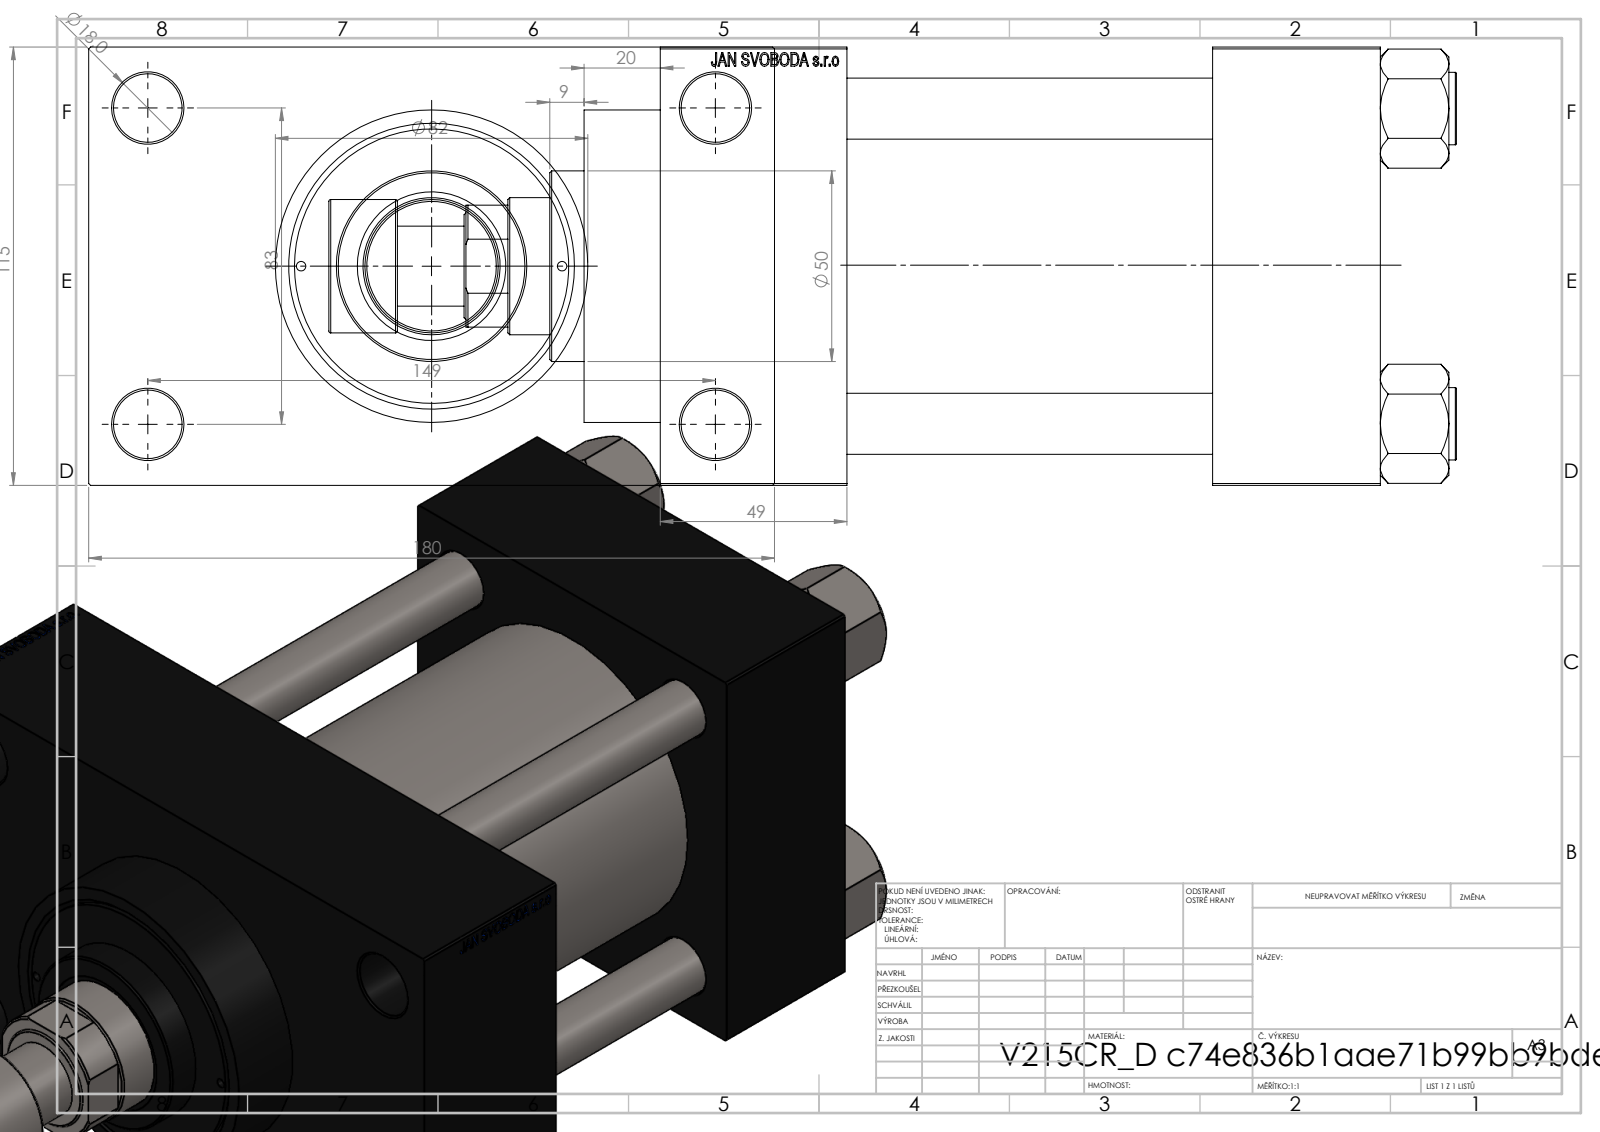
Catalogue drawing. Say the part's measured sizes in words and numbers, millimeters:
The part is named "V215CR_D_Body; V215_VC_A; V215CR_VCP_D; V215CR_D_TYCINKA (+2 more)". Its 3-D file was written by "SolidWorks 2019 (CONFIG_CONTROL_DESIGN)". It is 12 solids with 1173 faces: 551 planar, 96 cylindrical and 526 other. Overall it measures 296 by 180 by 115 millimeters. Its volume is 2 081 000 cubic millimeters and its surface area 327 114 square millimeters. Round holes: 4 of diameter 16, 4 of diameter 18, 2 of diameter 2.5, 2 of diameter 7, 2 of diameter 26.44, 2 of diameter 35, 1 of diameter 25.5, 1 of diameter 36, 1 of diameter 39, 1 of diameter 61, 1 of diameter 72, 1 of diameter 80. Round bosses or shafts: 4 of diameter 19, 1 of diameter 86, 1 of diameter 82, 1 of diameter 50, 1 of diameter 35, 1 of diameter 21. The main face-to-face distances are 115, 96, 49, 145, 44, 140, 189, 32.5, 147.5, 180. The hole center spacings are 33.15, 41.96, 57.81, 58.48, 82.7, 85.28, 86.17, 89.24.
